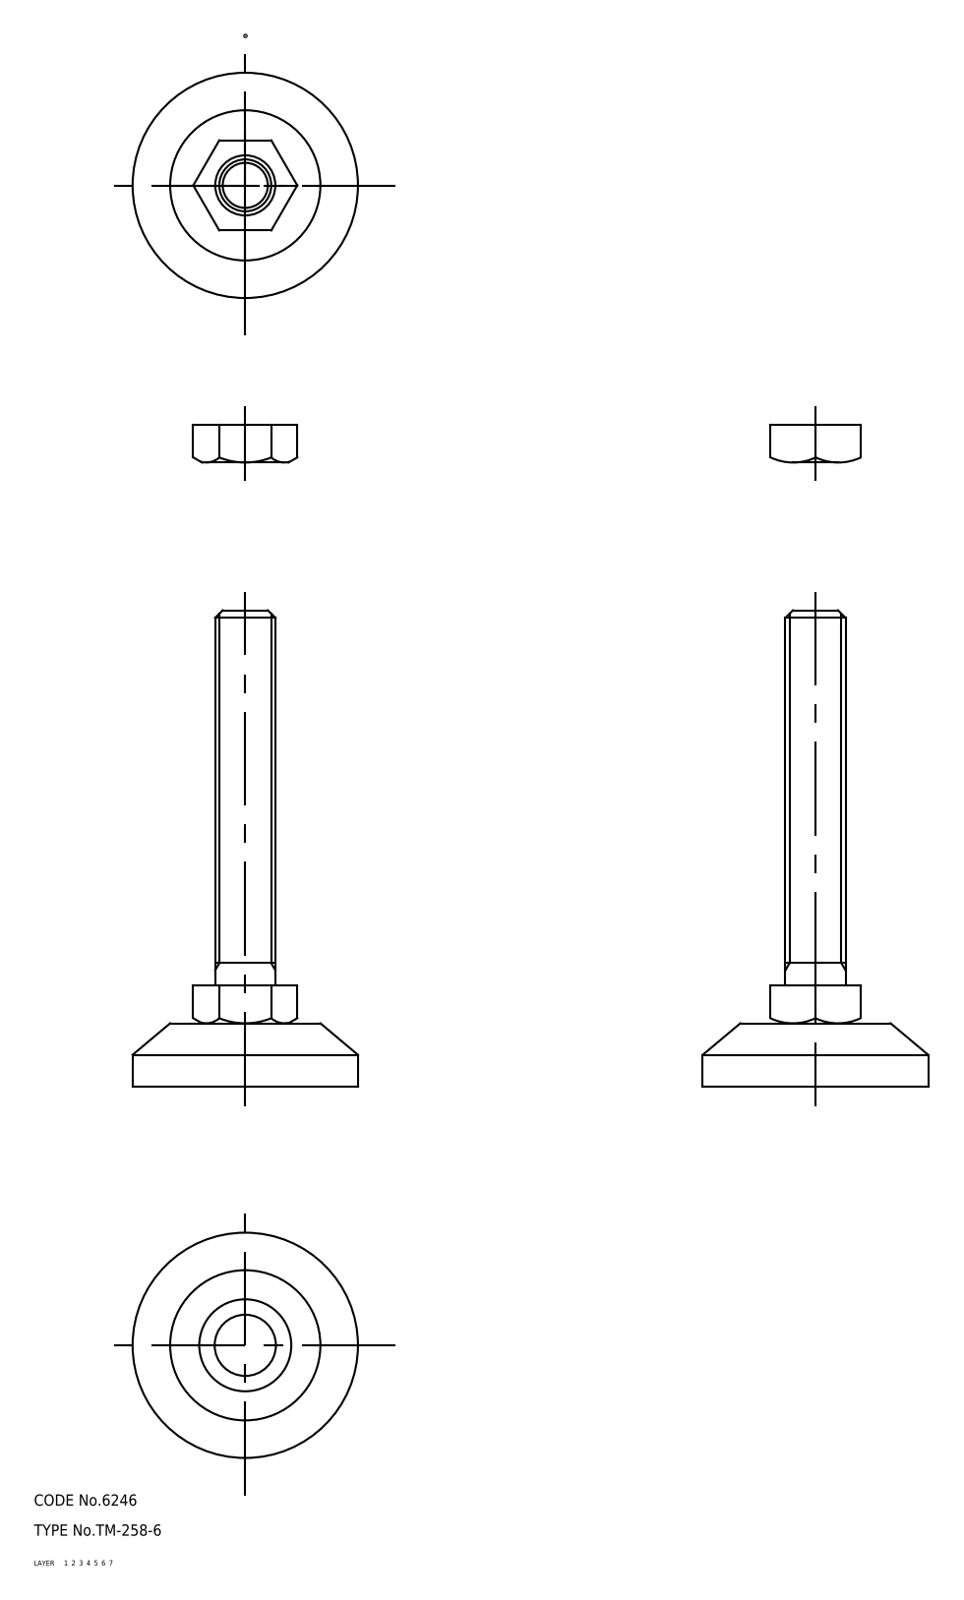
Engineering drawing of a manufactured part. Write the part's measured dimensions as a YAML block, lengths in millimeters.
part_name: "67112301; 67112314; 67112327"
step_written_by: "CADfix (AUTOMOTIVE_DESIGN)"
units: millimeters
bodies: {solids: 3, faces: 67, planar: 0, cylindrical: 0, other: 67}
overall_size: [127, 60, 60]
volume: 60103
surface_area: 18080
